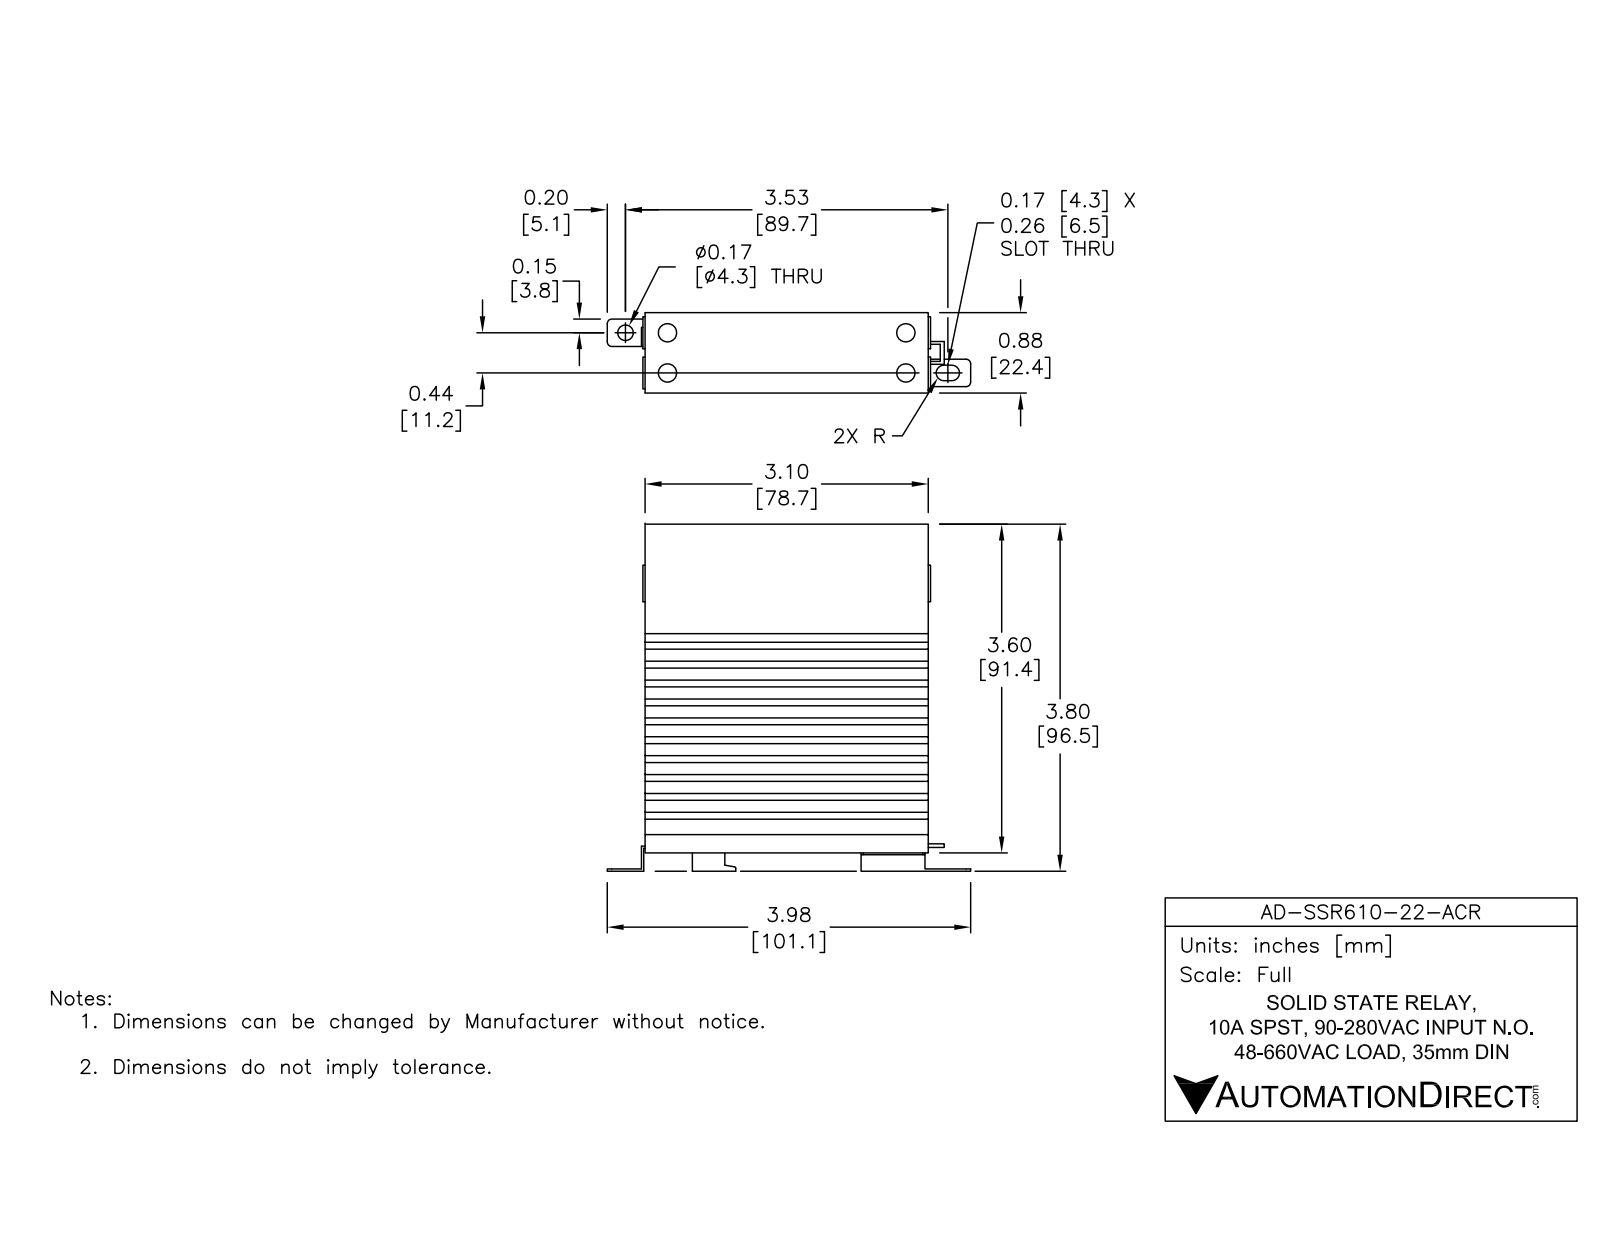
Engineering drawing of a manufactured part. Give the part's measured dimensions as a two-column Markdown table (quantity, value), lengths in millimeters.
| quantity | value |
| --- | --- |
| part name | AD-SSR610-22-ACR |
| STEP written by | SolidWorks 2014 (AUTOMOTIVE_DESIGN) |
| units | millimeters |
| bodies | 1 solid, 215 faces (195 planar, 20 cylindrical, 0 other) |
| overall size | 101.1 × 96.5 × 22.4 |
| volume | 116 900 mm³ |
| surface area | 48 330 mm² |
| round holes (diameter × count) | 5.1 × 4, 4.3 × 1 |
| partial cylindrical surfaces (radius × count) | 1.3 × 6, 2.2 × 2, 0.4 × 1 |
| main face-to-face distances | 15.7, 5.3, 21, 10.5, 3.4, 12.4, 8.6, 10.5, 1.9, 5.3 |
| hole center spacings | 11.2, 66.3, 67.2, 11.7, 16.2, 78, 78.8 |
